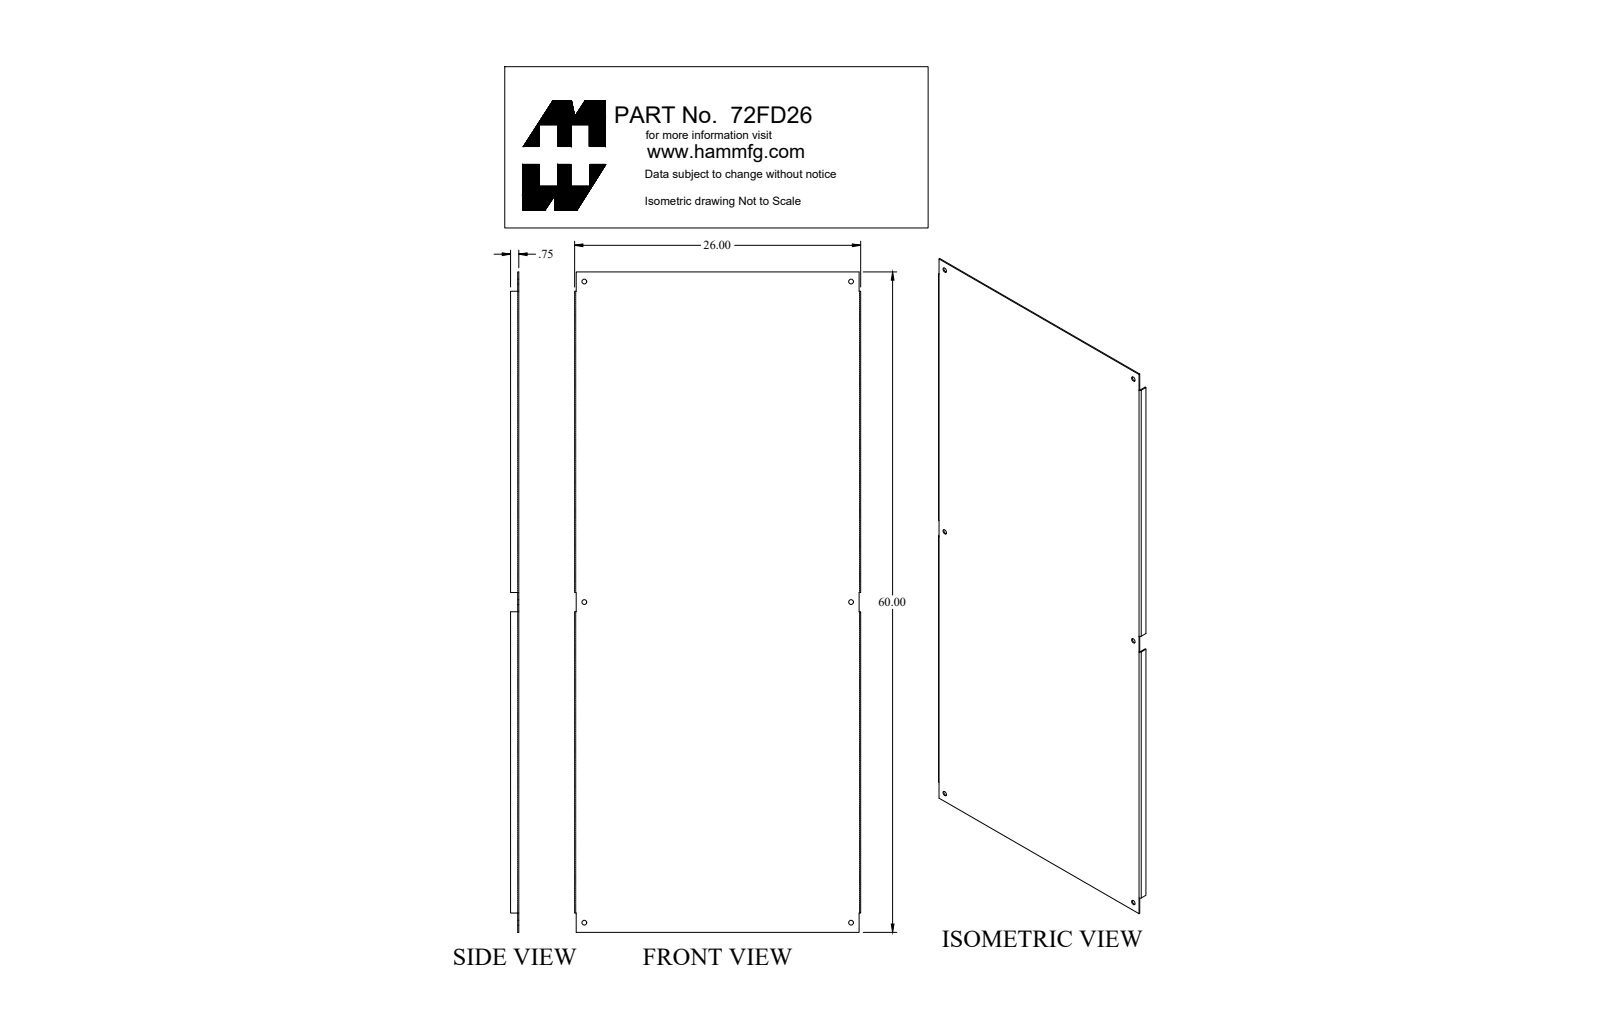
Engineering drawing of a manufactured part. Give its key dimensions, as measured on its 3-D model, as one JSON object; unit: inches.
{"part_name": "72FD26_Default", "step_written_by": "SolidWorks 2018 (CONFIG_CONTROL_DESIGN)", "units": "inches", "bodies": {"solids": 1, "faces": 50, "planar": 30, "cylindrical": 20, "other": 0}, "overall_size": [60, 26, 0.75], "volume_in3": 154.4, "surface_area_in2": 3267, "round_holes": [[0.437, 6]], "partial_cylinders_radius": [[0.048, 2], [0.143, 2]], "face_to_face_distances": [0.095, 25.905, 26, 25.81, 0.75, 0.655, 60, 0.143, 25.857, 0.048], "hole_center_spacings": [29.125, 37.899, 24.25, 58.25, 63.096]}
